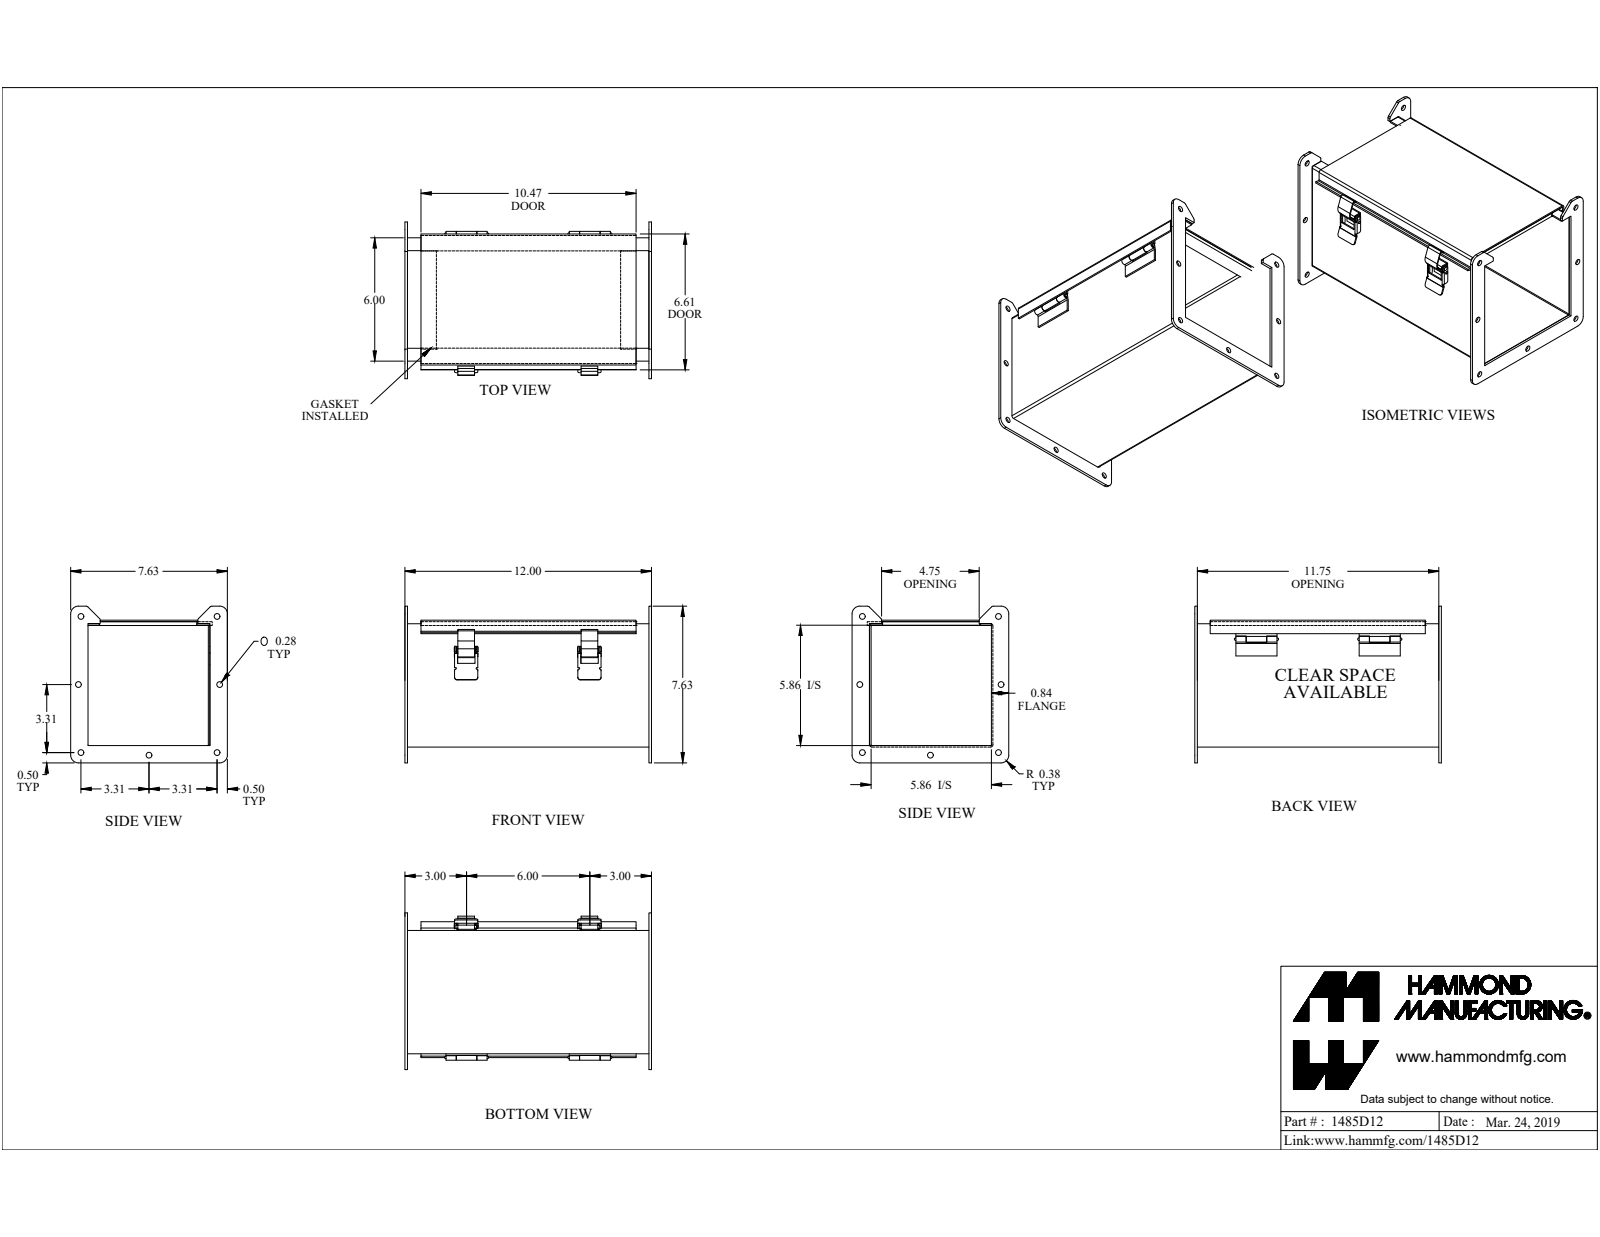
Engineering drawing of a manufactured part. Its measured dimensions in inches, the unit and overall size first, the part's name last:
Units: inches
Overall size (bounding box): 12 × 7.625 × 7.625
Round holes (diameter × count): ⌀0.281 ×7, ⌀0.125 ×1, ⌀0.13 ×1, ⌀0.164 ×1
Round bosses / shafts (diameter × count): ⌀0.187 ×2, ⌀0.275 ×1, ⌀0.156 ×1, ⌀0.125 ×1, ⌀0.125 ×1
Partial cylindrical surfaces — rounded edges, fillets, slot ends (radius × count): R0.016 ×13, R0.125 ×9, R0.036 ×7, R0.108 ×7, R0.035 ×5, R0.039 ×5, R0.076 ×5, R0.015 ×4
Main face-to-face distances: 0.072, 5.928, 6.1, 6, 5.856, 6.028, 6.172, 0.125, 11.875, 0.172
Hole centre spacings: 7.519, 6.625, 3.315, 3.315, 9.369, 0.285, 1.112, 1.459
Volume: 31.62 in³ · Surface area: 793.5 in²
Bodies: 20 solids, 416 faces (250 planar, 162 cylindrical, 4 other)
Part name (STEP PRODUCT): 1485D12
STEP written by: SolidWorks 2019 (CONFIG_CONTROL_DESIGN)
